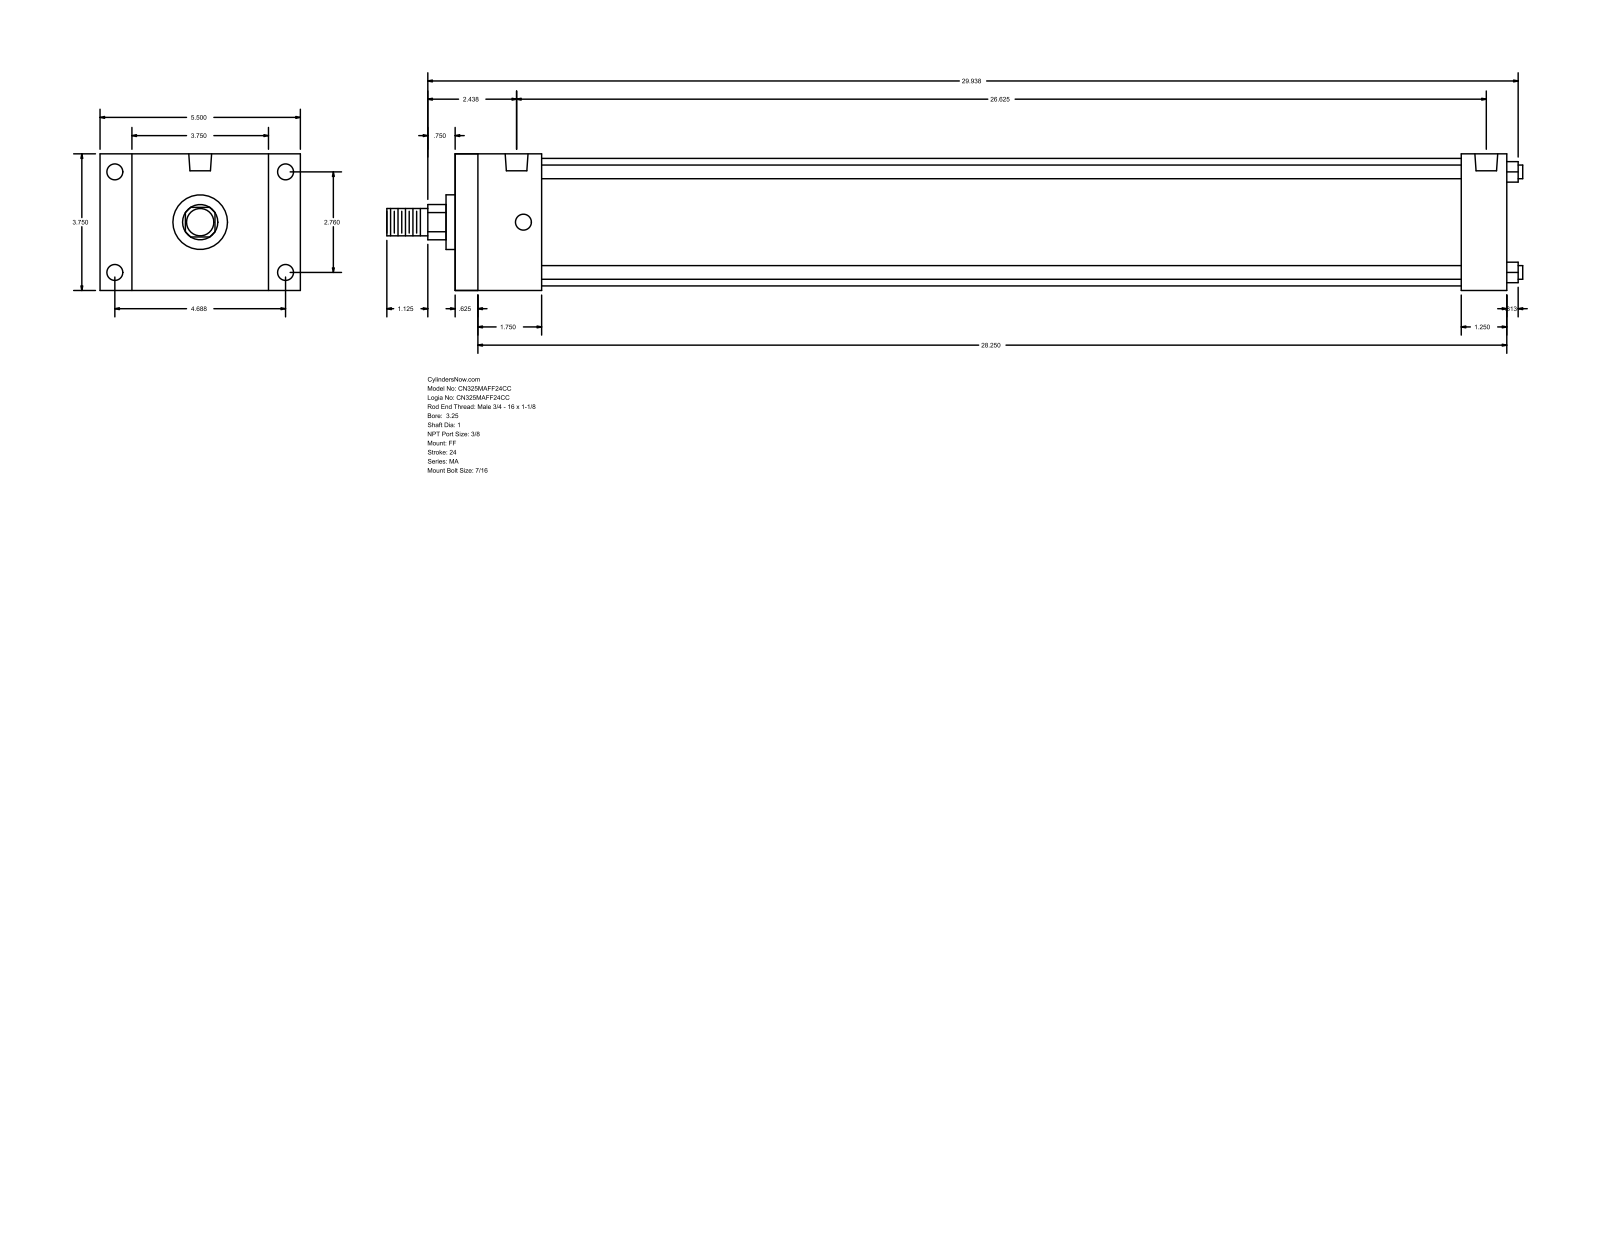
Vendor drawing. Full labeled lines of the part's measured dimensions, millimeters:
Part name (STEP PRODUCT): MA_FF__0325_1
STEP written by: GSSL Pune (CONFIG_CONTROL_DESIGN)
Units: millimetres
Bodies: 0 solids, 92 faces (64 planar, 28 cylindrical, 0 other)
Overall size (bounding box): 792.16 × 139.7 × 95.25
Round holes (diameter × count): ⌀11.11 ×8, ⌀15.93 ×2
Round bosses / shafts (diameter × count): ⌀9.53 ×4, ⌀88.9 ×1, ⌀38.1 ×1, ⌀25.4 ×1, ⌀19.05 ×1
Partial cylindrical surfaces — rounded edges, fillets, slot ends (radius × count): R12.29 ×1
Main face-to-face distances: 95.24, 733.43, 15.87, 717.56, 22.23, 117.47, 60.33, 701.68, 44.46, 685.81
Hole centre spacings: 70.1, 119.06, 138.16, 666.75, 4.76, 4.77, 671.51, 671.52
